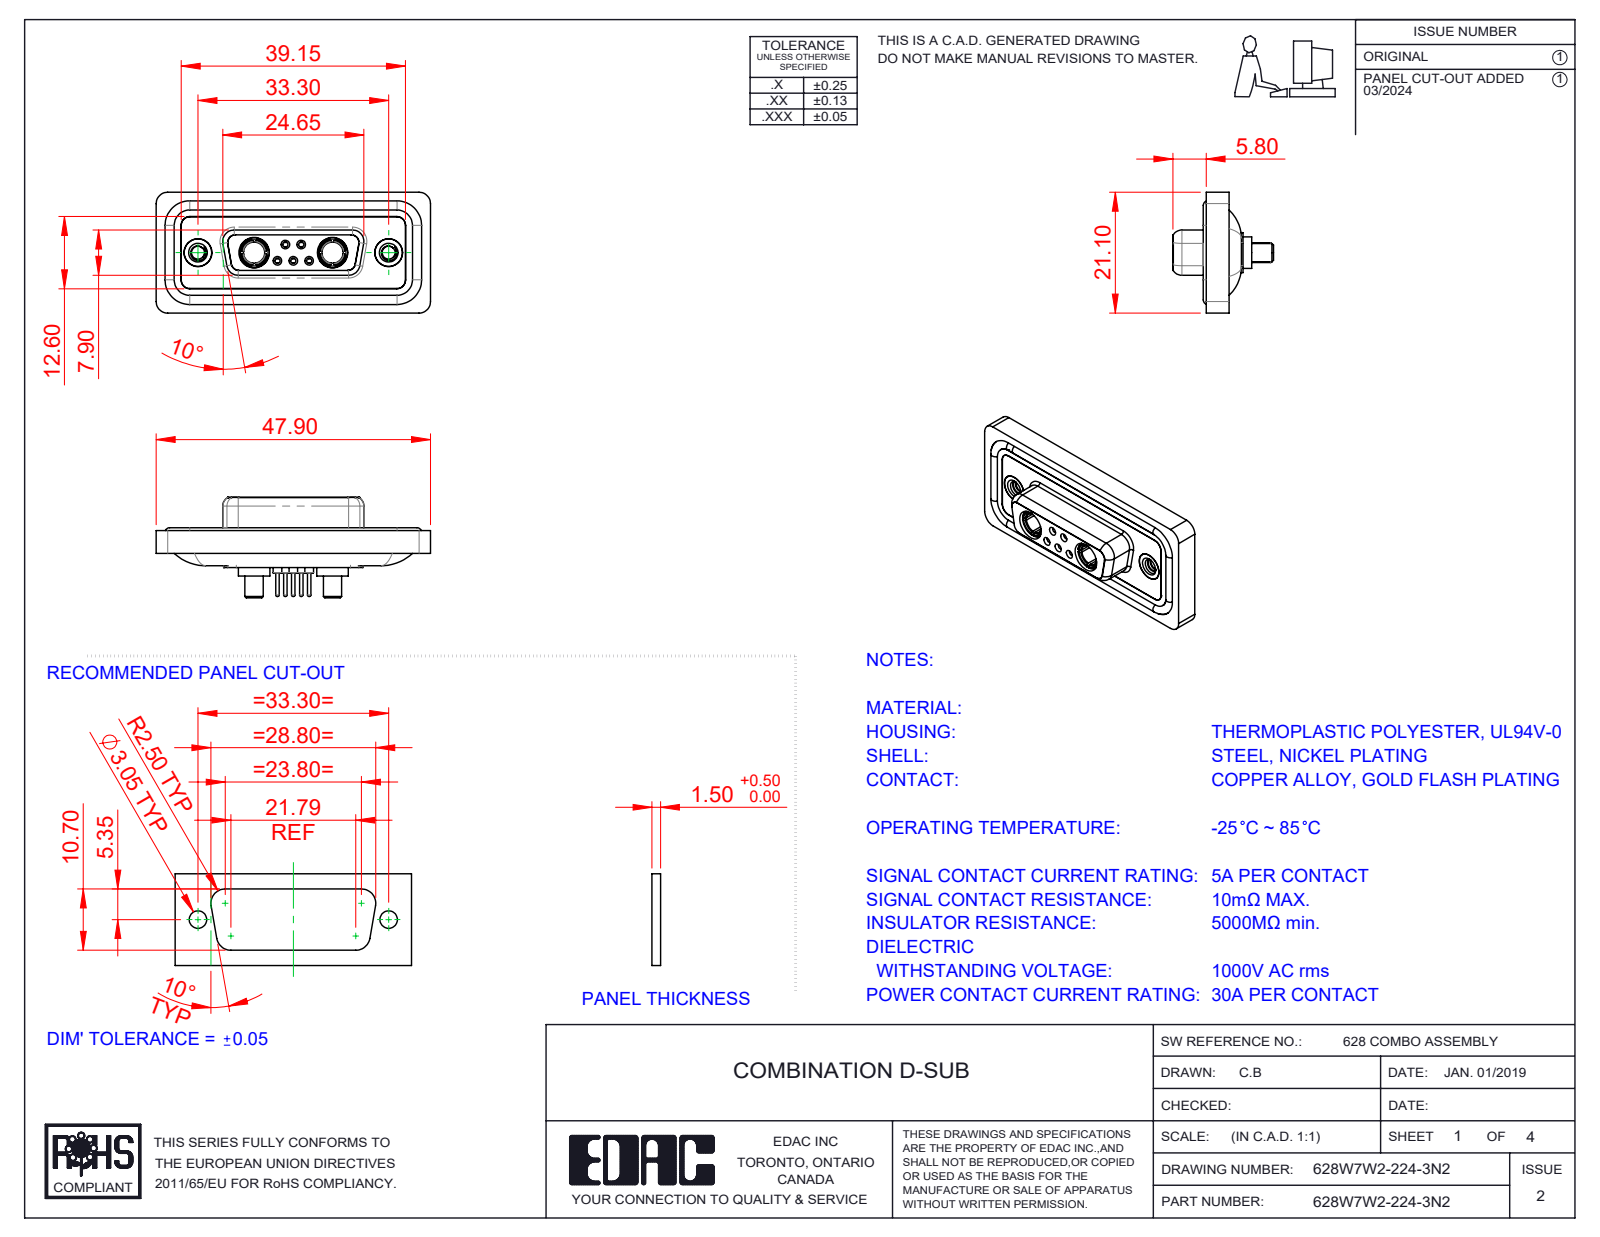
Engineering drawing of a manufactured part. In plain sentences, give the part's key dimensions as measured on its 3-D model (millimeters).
The part is named "628Combo Threaded Rivet_2; 628Combo Shell Front_15 Contacts; 628W7W2-224-3N2; 628Combo Contact Row 2_24 (+5 more)". Its 3-D file was written by "SolidWorks 2023 (CONFIG_CONTROL_DESIGN)". It is 16 solids with 809 faces: 238 planar, 329 cylindrical and 242 other. Overall it measures 47.9 by 21.1 by 17.55 millimeters. Its volume is 6 091 cubic millimeters and its surface area 9 894 square millimeters. Round holes: 5 of diameter 0.9, 5 of diameter 1.1, 5 of diameter 1.5, 5 of diameter 2, 4 of diameter 4.85, 3 of diameter 1.6, 2 of diameter 1.7, 2 of diameter 2.26, 2 of diameter 3.7, 2 of diameter 4, 2 of diameter 4.05, 2 of diameter 5. Round bosses or shafts: 6 of diameter 1.6, 5 of diameter 2.2, 5 of diameter 0.6, 2 of diameter 5.5, 2 of diameter 5.2, 2 of diameter 4.96, 2 of diameter 4.95, 2 of diameter 4.8. Partial cylindrical surfaces (rounded edges, fillets, slot ends): 22 of radius 1.5, 20 of radius 2, 12 of radius 1.35, 8 of radius 1.6, 4 of radius 0.25, 4 of radius 0.5, 4 of radius 0.6, 4 of radius 0.65. The main face-to-face distances are 0.4, 1.8, 1.6, 0.5, 2.9, 7.45, 1.1, 5.65, 6.6, 7.05. The hole center spacings are 3.16, 2.77, 9.8, 23.5, 4.31, 4.33, 5.03, 5.04.
